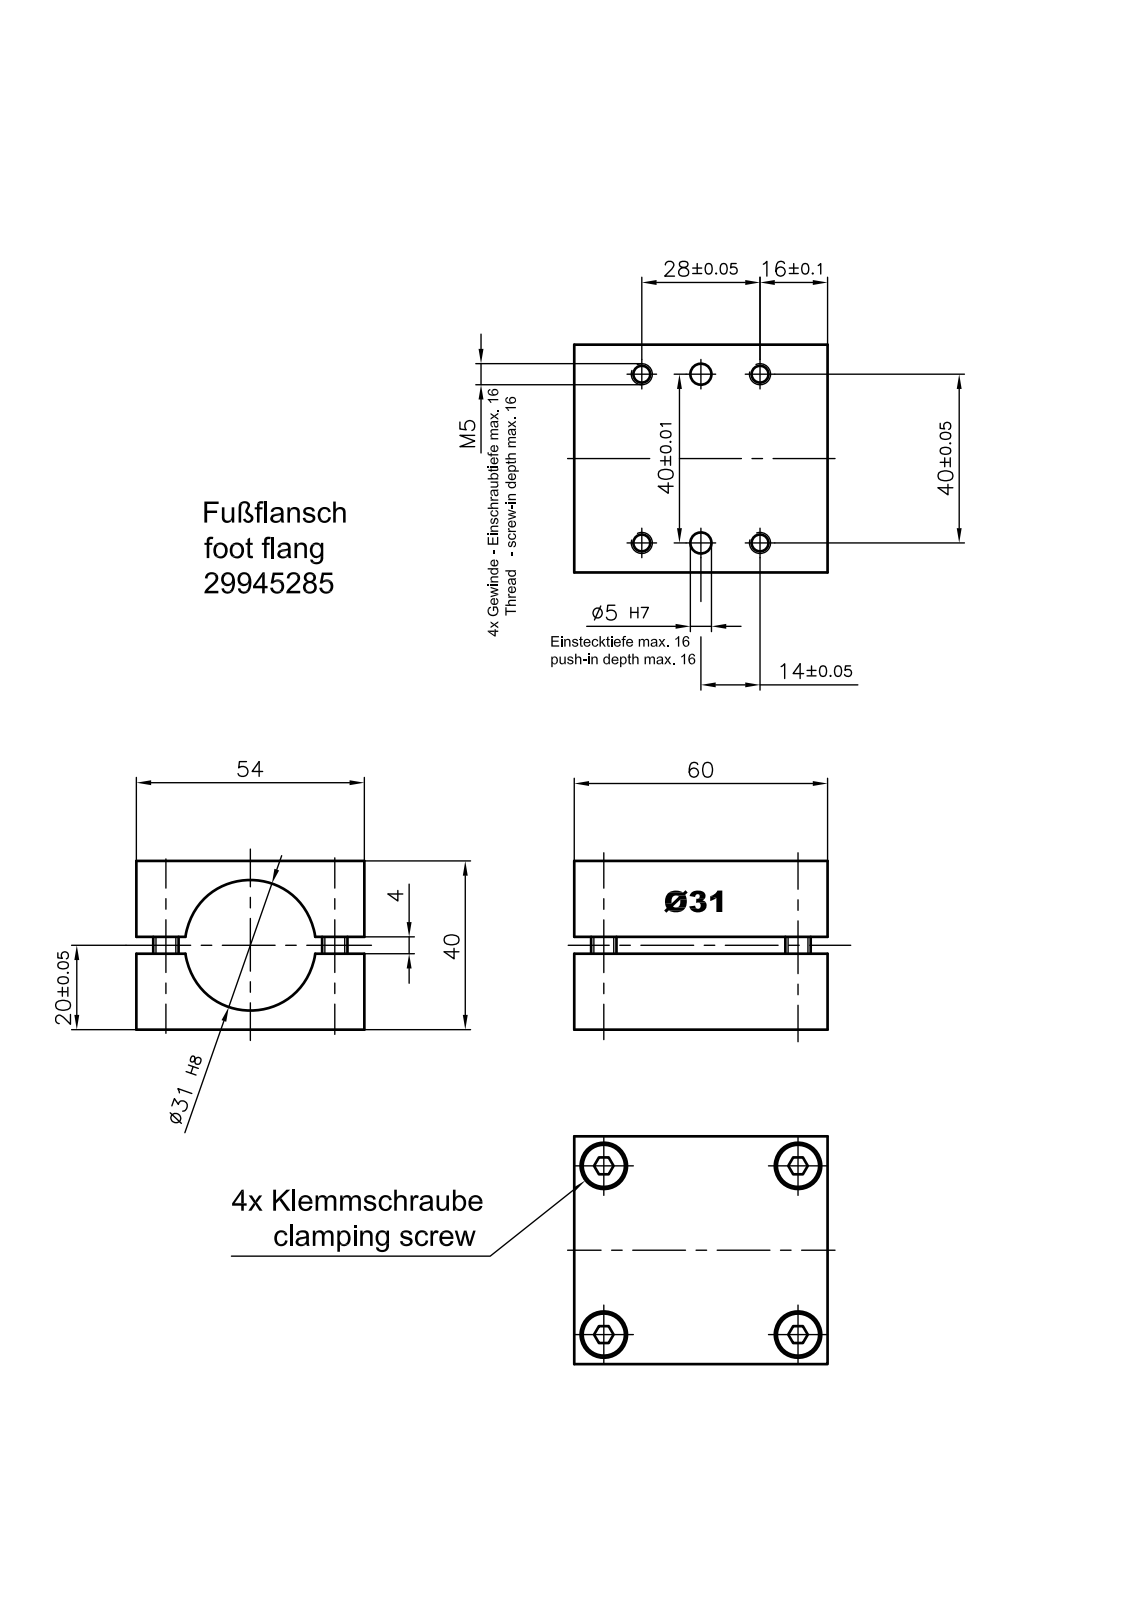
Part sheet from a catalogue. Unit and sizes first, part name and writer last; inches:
Units: inches
Overall size (bounding box): 2.362 × 2.126 × 1.575
Round holes (diameter × count): ⌀1.22 ×1
Round bosses / shafts (diameter × count): ⌀0.394 ×4, ⌀0.236 ×4
Main face-to-face distances: 1.575, 0.709, 0.866, 2.126, 2.362, 0.157, 0.197, 0.551, 1.417, 1.339
Volume: 4.653 in³ · Surface area: 41.7 in²
Bodies: 1 solid, 94 faces (50 planar, 10 cylindrical, 34 other)
Part name (STEP PRODUCT): 29945285 \S\X31 Fu\S\_flansch
STEP written by: Autodesk Inventor 2008 (AUTOMOTIVE_DESIGN)
